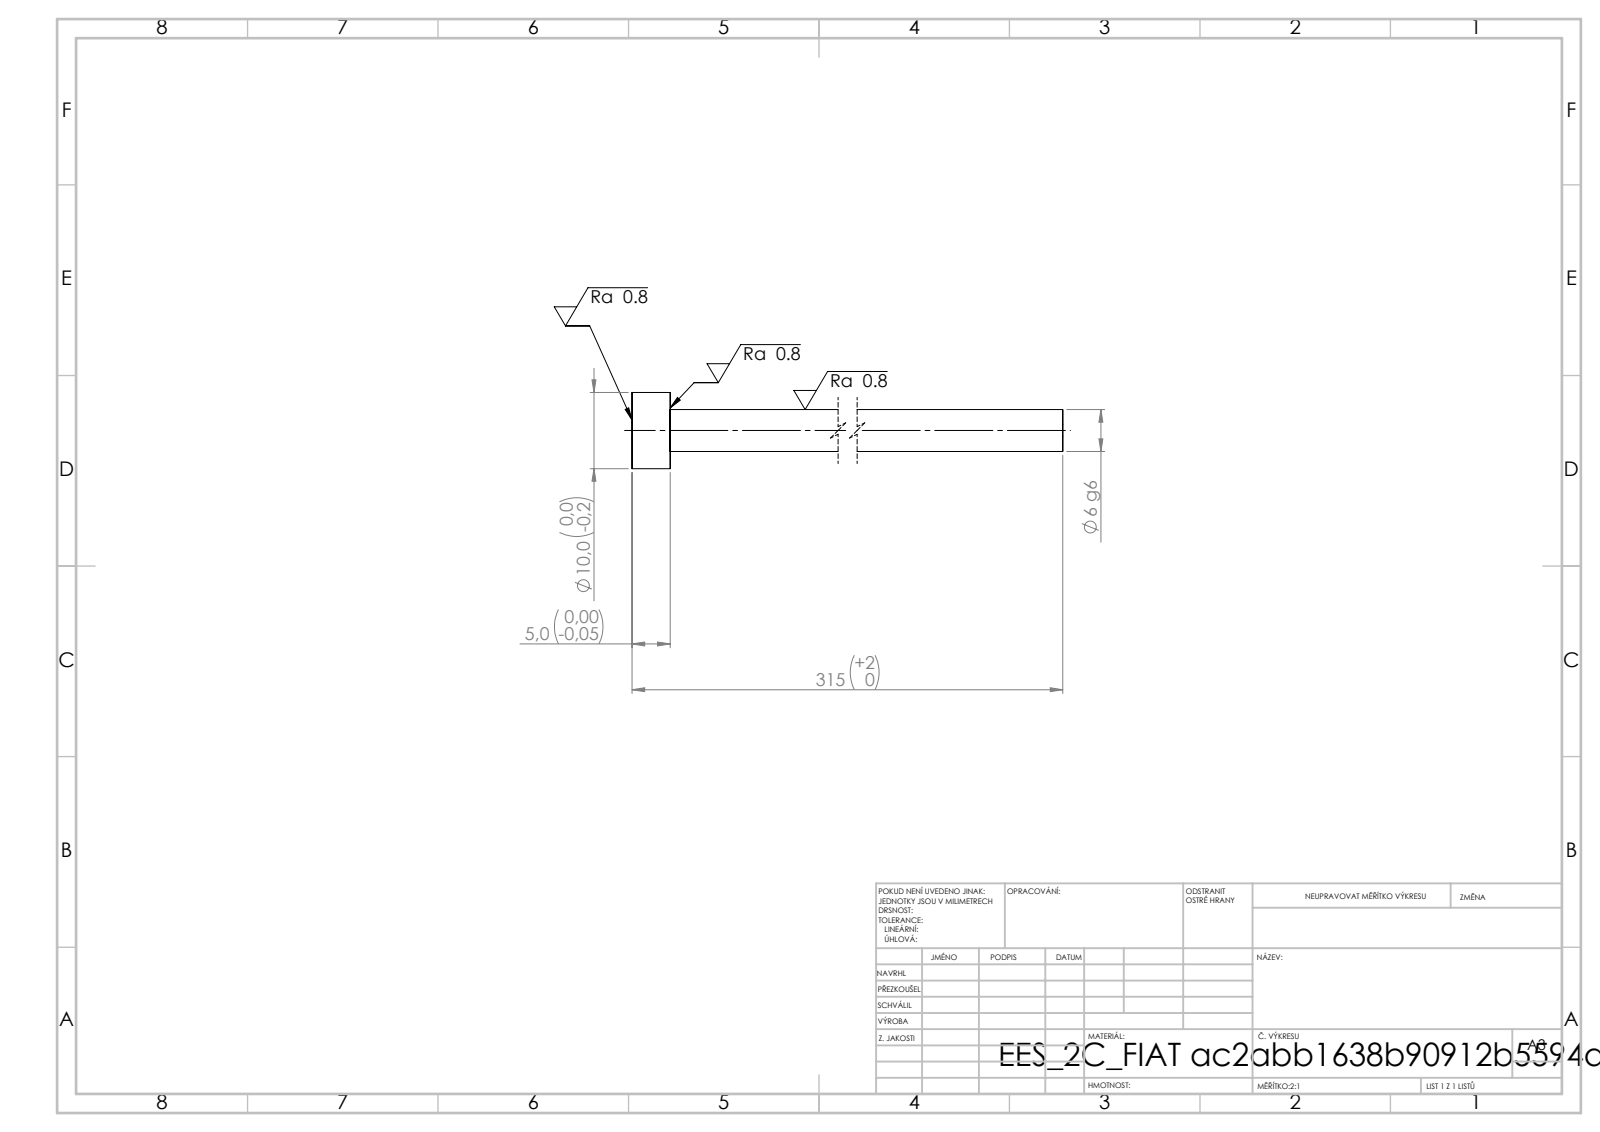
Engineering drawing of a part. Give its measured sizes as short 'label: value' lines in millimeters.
written by: SolidWorks 2019 (CONFIG_CONTROL_DESIGN)
unit: mm
bodies: 1 solid, 7 faces (3 planar, 4 cylindrical, 0 other)
size: 315 × 10 × 10
volume: 7 758 mm³; area: 5 671 mm²
bosses: 1× ⌀10, 1× ⌀5.5
face distances: 5, 315, 310
